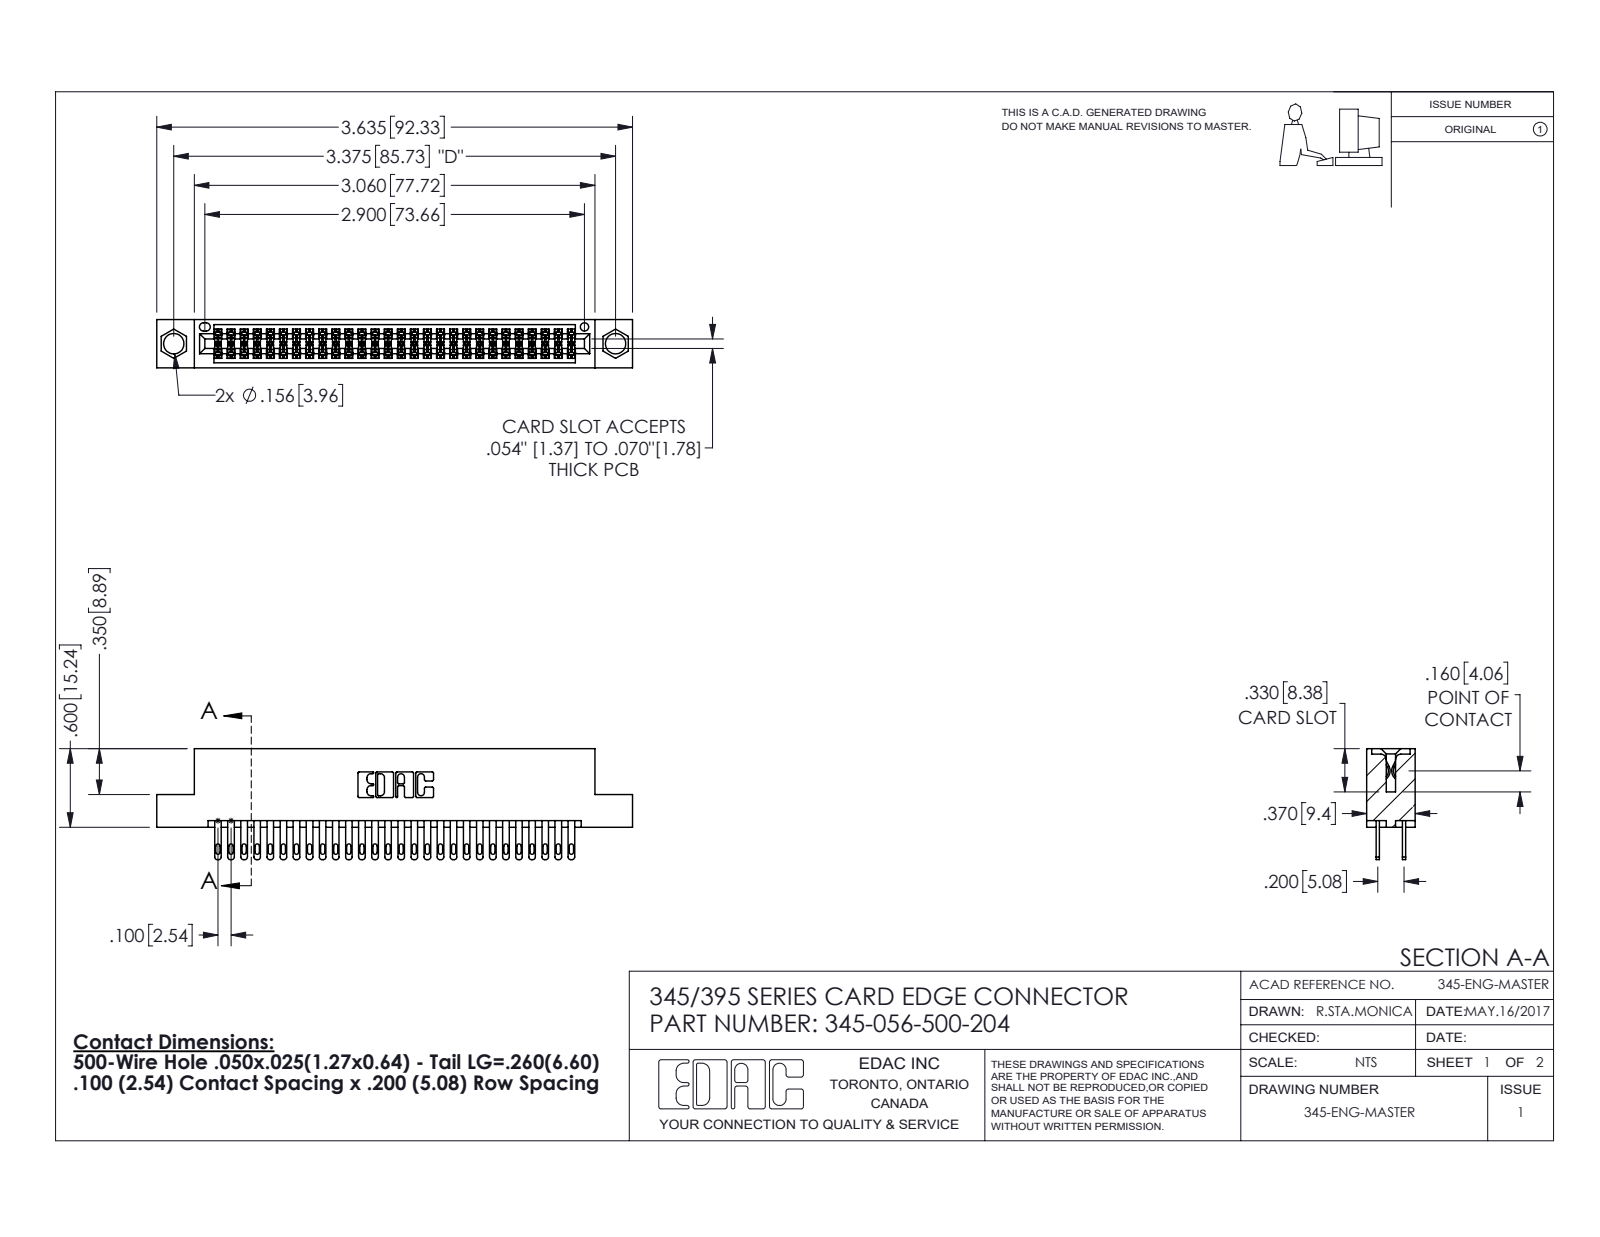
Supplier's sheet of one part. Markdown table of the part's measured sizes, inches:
| quantity | value |
| --- | --- |
| part name | 345-292-001_345-293-100; 345-056-500-204; 345 Part_Flush Mounting Lugs - 0.156 Dia-TI |
| STEP written by | SolidWorks 2020 (CONFIG_CONTROL_DESIGN) |
| units | inches |
| bodies | 57 solids, 2716 faces (1606 planar, 1110 cylindrical, 0 other) |
| overall size | 3.635 × 0.847 × 0.37 |
| volume | 0.543 in³ |
| surface area | 20.64 in² |
| round holes (diameter × count) | 0.156 × 2, 0.064 × 1 |
| partial cylindrical surfaces (radius × count) | 0.006 × 84, 0.016 × 56, 0.02 × 56, 0.01 × 22, 0.007 × 6, 0.031 × 6, 0.026 × 3, 0.014 × 2 |
| main face-to-face distances | 0.298, 0.072, 0.2, 0.098, 0.272, 0.025, 0.37, 0.225, 0.175, 0.149 |
| hole center spacings | 0.27, 3.14, 3.375 |
